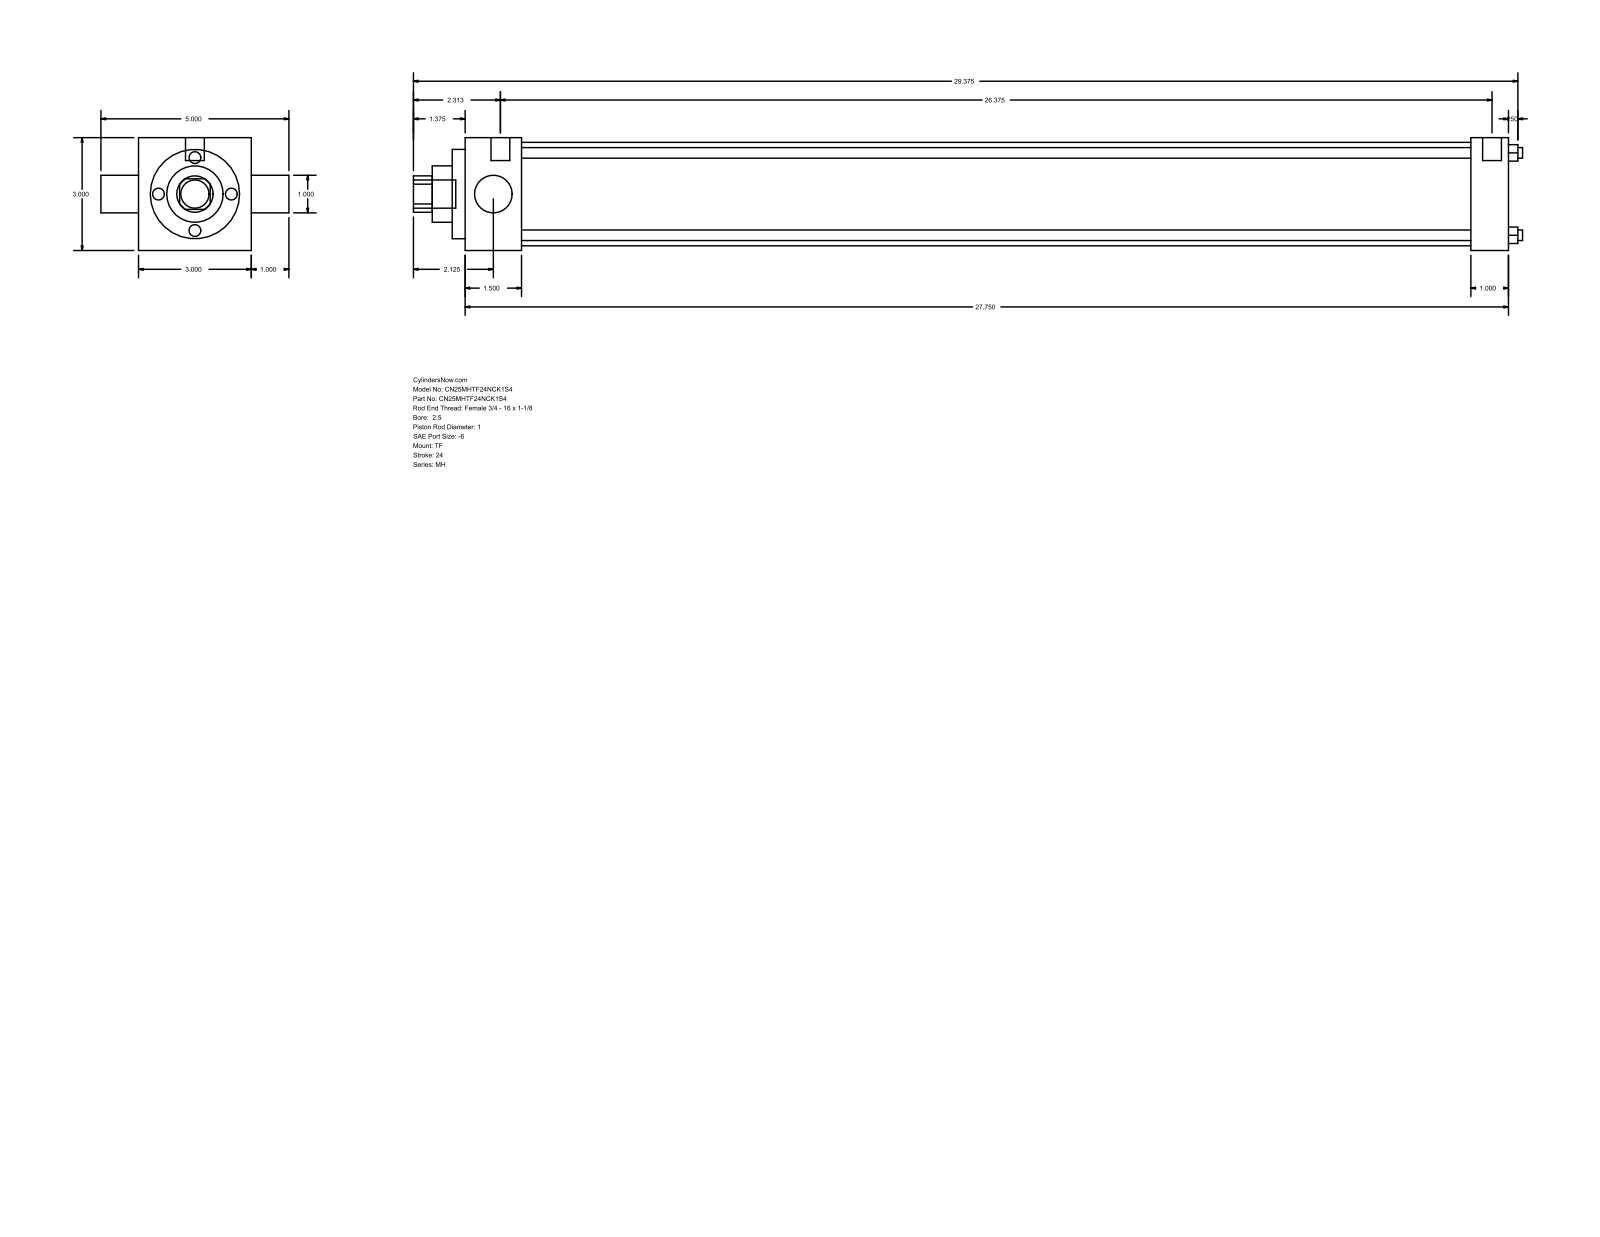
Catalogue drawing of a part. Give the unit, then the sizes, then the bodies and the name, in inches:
Units: inches
Overall size (bounding box): 29.5 × 5 × 3
Round holes (diameter × count): ⌀0.281 ×4, ⌀1 ×2, ⌀1.5 ×1, ⌀2.375 ×1, ⌀2.75 ×1
Round bosses / shafts (diameter × count): ⌀0.219 ×3, ⌀0.5 ×2, ⌀0.75 ×1
Partial cylindrical surfaces — rounded edges, fillets, slot ends (radius × count): R0.484 ×1
Main face-to-face distances: 3, 27.75, 1, 1.5, 26.25, 26.75, 25.25, 0.344, 1.844, 27.094
Hole centre spacings: 1.548, 2.19, 3.097
Bodies: 0 solids, 86 faces (61 planar, 25 cylindrical, 0 other)
Part name (STEP PRODUCT): MH_TF__0250_1
STEP written by: GSSL Pune (CONFIG_CONTROL_DESIGN)
